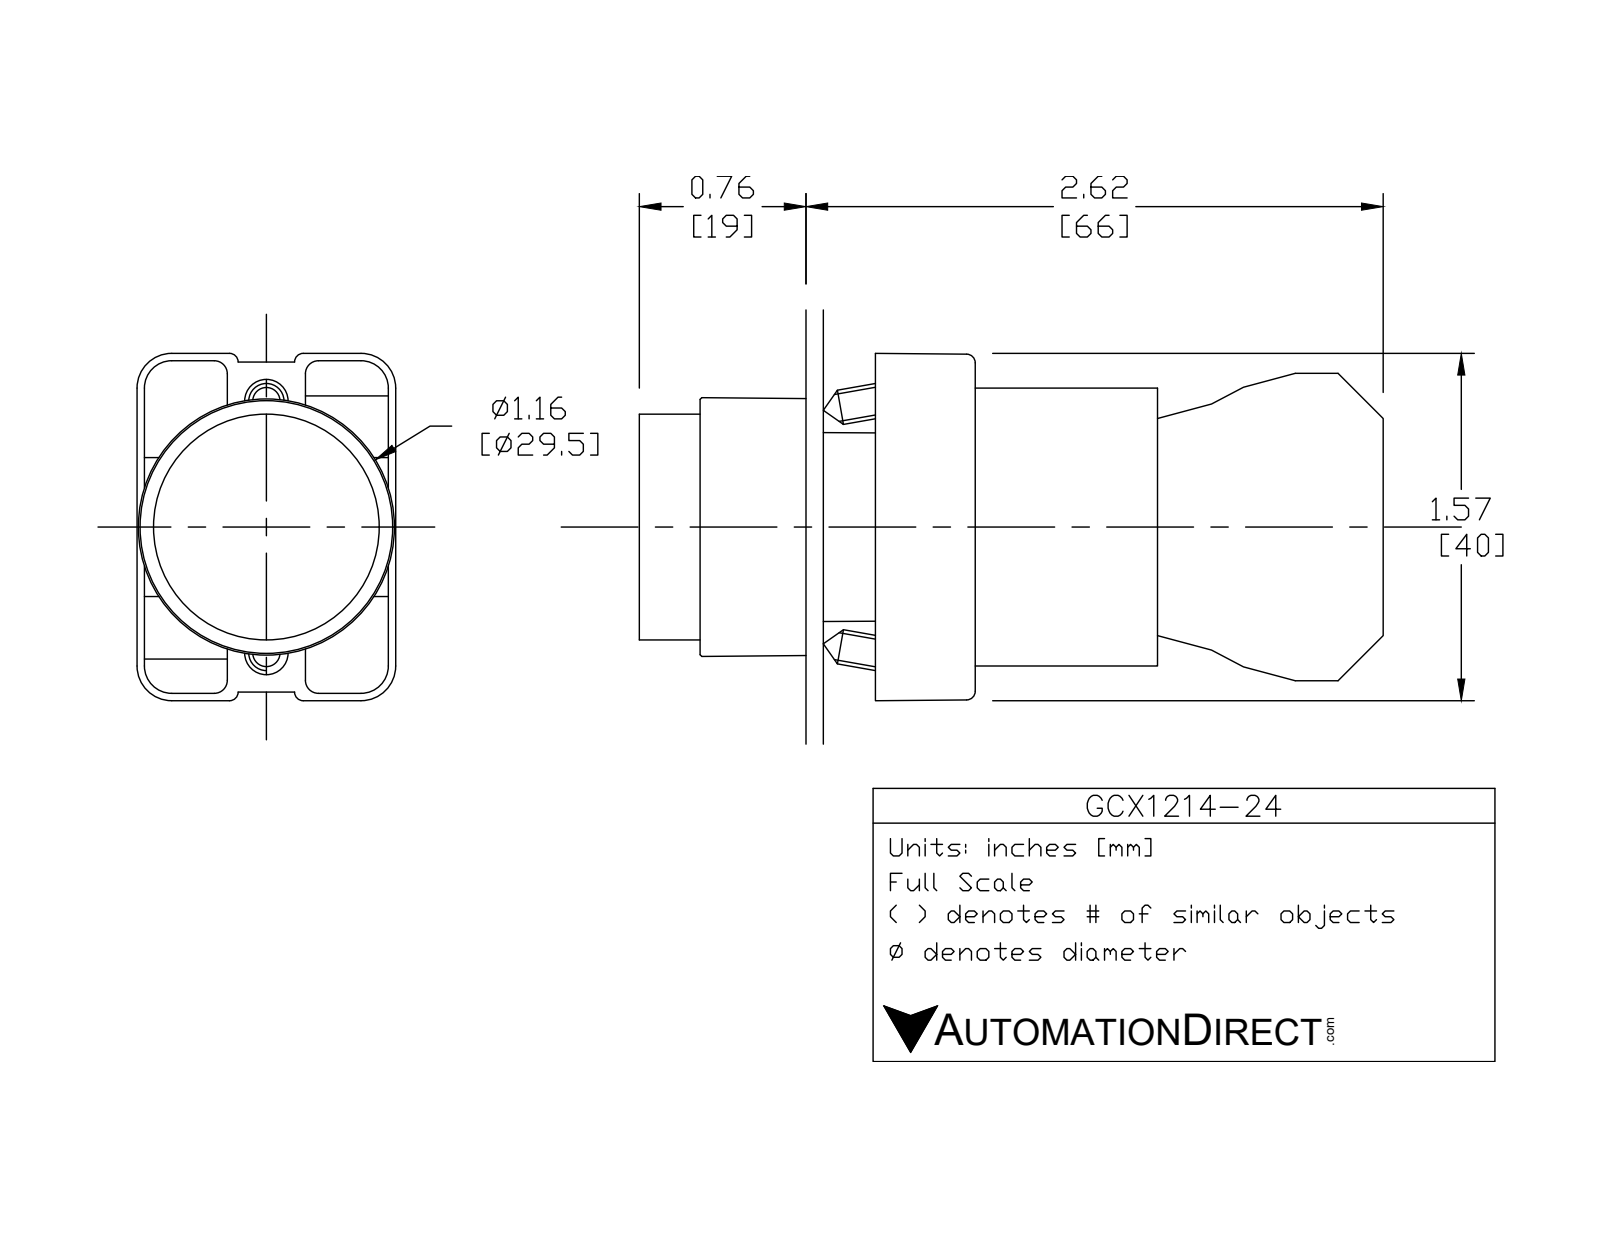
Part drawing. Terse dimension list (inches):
name: ecx1029; ecx1040; GCX1214 OPERATOR; ECX1050 (+1 more)
written by: SolidWorks 2016 (AUTOMOTIVE_DESIGN)
unit: in
bodies: 7 solids, 425 faces (250 planar, 144 cylindrical, 31 other)
size: 3.319 × 1.581 × 1.177
volume: 2.721 in³; area: 36.32 in²
holes: 2× ⌀0.079, 2× ⌀0.124, 2× ⌀0.13, 1× ⌀0.087, 1× ⌀0.197, 1× ⌀0.469, 1× ⌀0.878, 1× ⌀0.888, 1× ⌀1.024
bosses: 4× ⌀0.157, 1× ⌀1.175, 1× ⌀1.004, 1× ⌀0.945, 1× ⌀0.856, 1× ⌀0.78, 1× ⌀0.504
rounds: 24× R0.059, 12× R0.041, 12× R0.124, 12× R0.157, 8× R0.039, 2× R0.128, 1× R0.02, 1× R0.063
face distances: 0.827, 0.579, 1.171, 2.02, 1.193, 0.031, 0.033, 0.573, 1.165, 0.593
hole spacings: 0.236, 0.544, 0.472, 0.49
